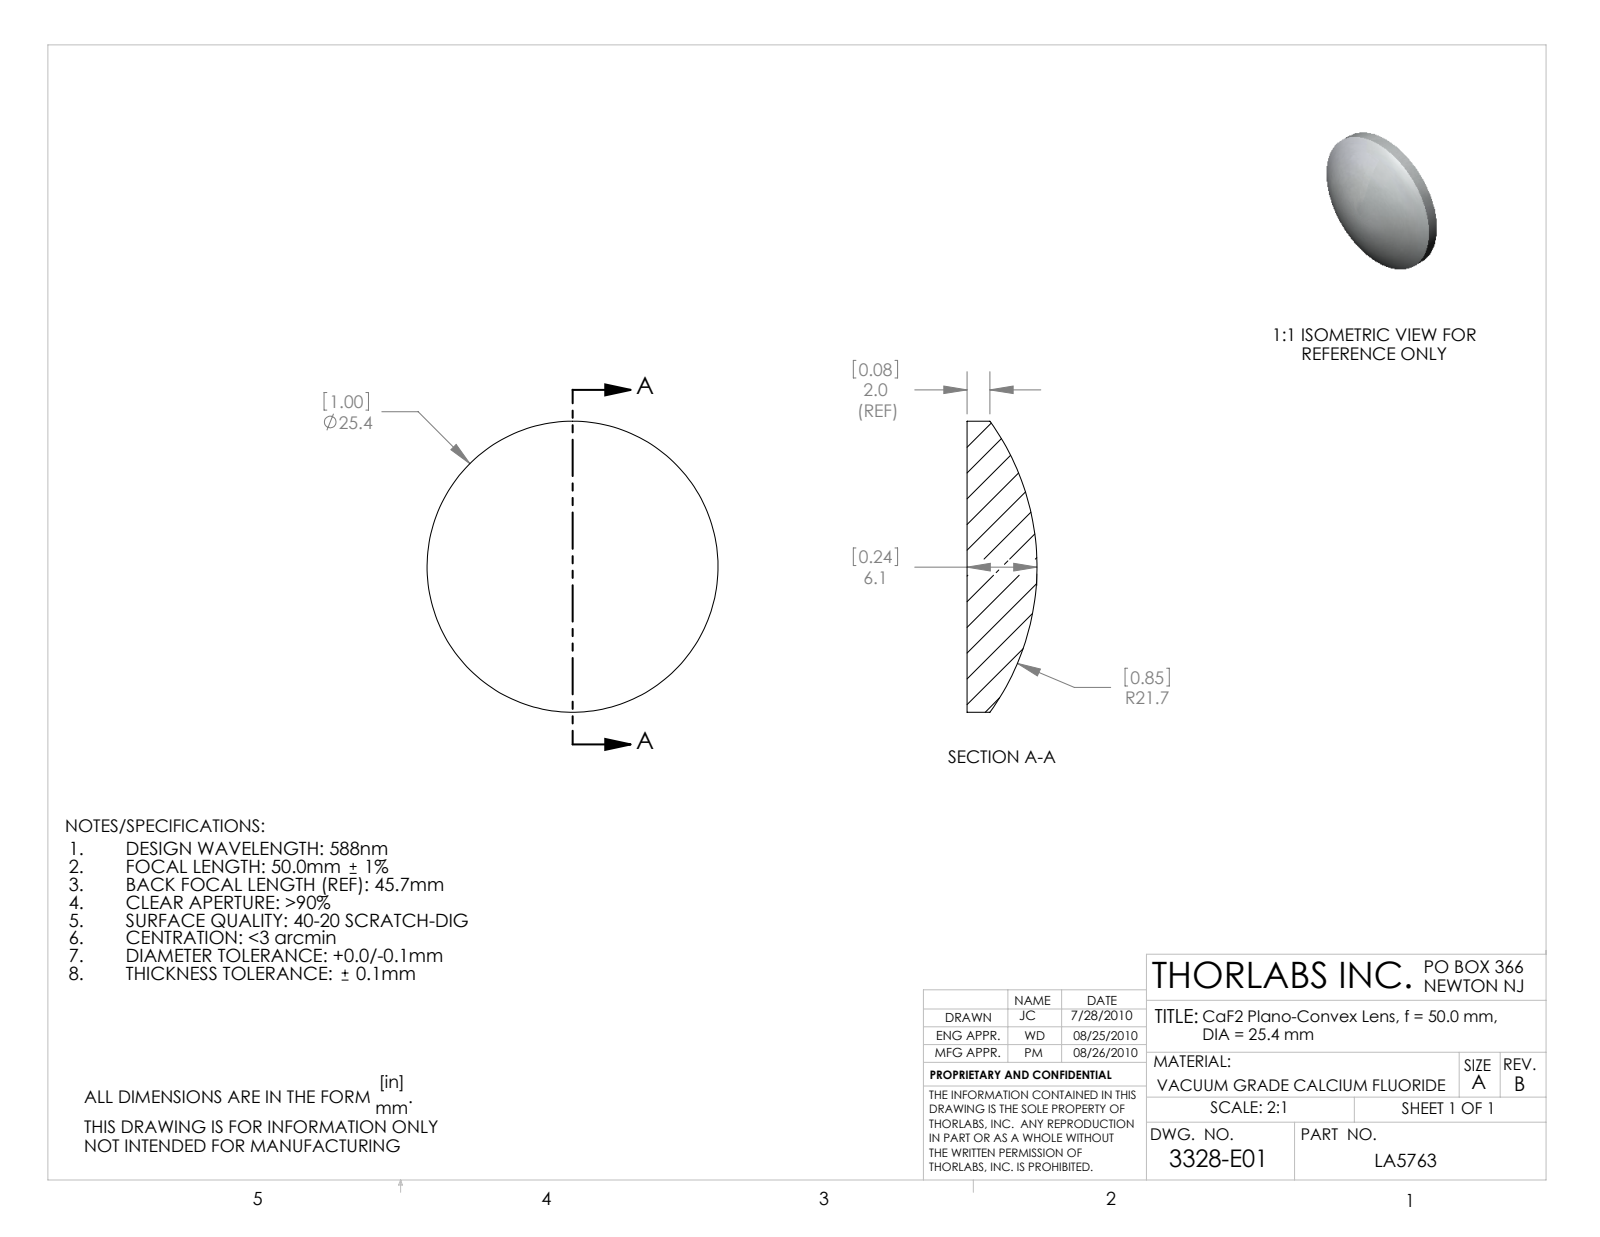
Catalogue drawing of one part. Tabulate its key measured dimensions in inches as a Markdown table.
| quantity | value |
| --- | --- |
| part name | 3328-E0W |
| STEP written by | SolidWorks 2009 (AUTOMOTIVE_DESIGN) |
| units | inches |
| bodies | 1 solid, 5 faces (1 planar, 2 cylindrical, 2 other) |
| overall size | 1 × 1 × 0.296 |
| volume | 0.152 in³ |
| surface area | 1.966 in² |
| round bosses / shafts (diameter × count) | 1 × 1 |
